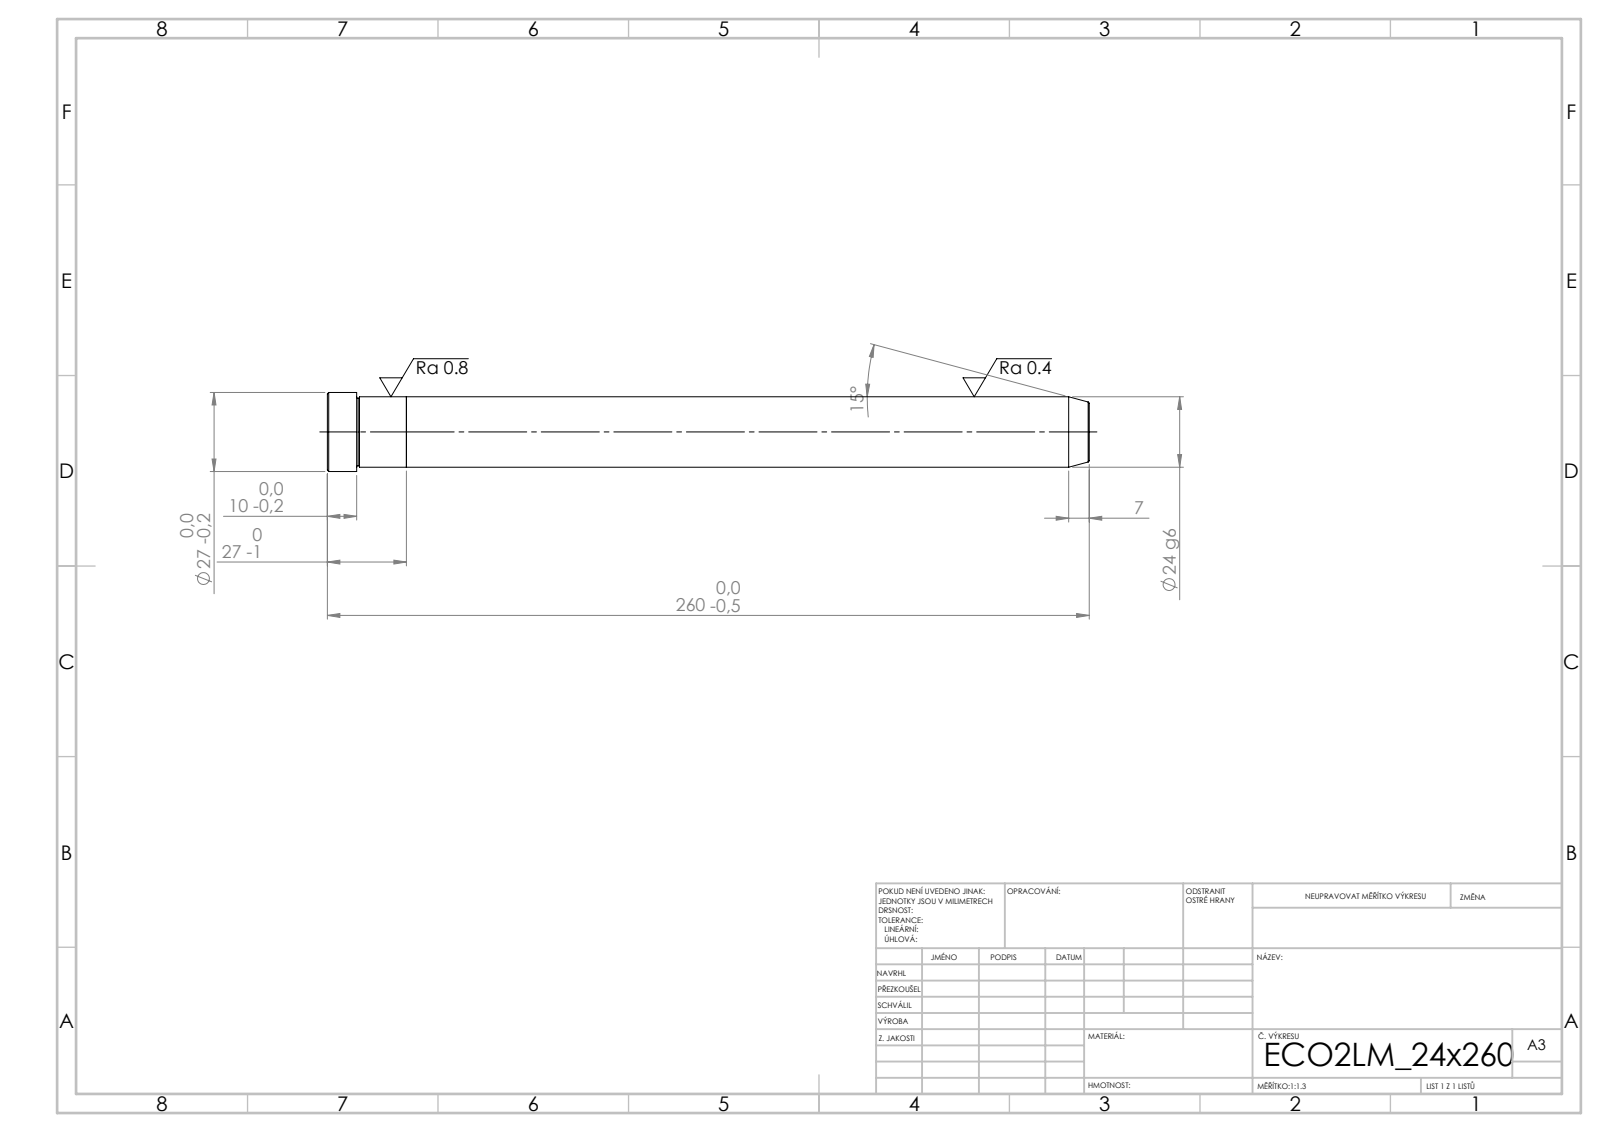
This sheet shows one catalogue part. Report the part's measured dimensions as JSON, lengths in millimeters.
{"step_written_by": "SolidWorks 2019 (CONFIG_CONTROL_DESIGN)", "units": "millimeters", "bodies": {"solids": 2, "faces": 21, "planar": 5, "cylindrical": 6, "other": 10}, "overall_size": [260, 27, 27], "volume_mm3": 118312, "surface_area_mm2": 21601, "round_bosses_or_shafts": [[27, 1], [24, 1]], "face_to_face_distances": [27, 233, 260, 250, 17, 10]}
